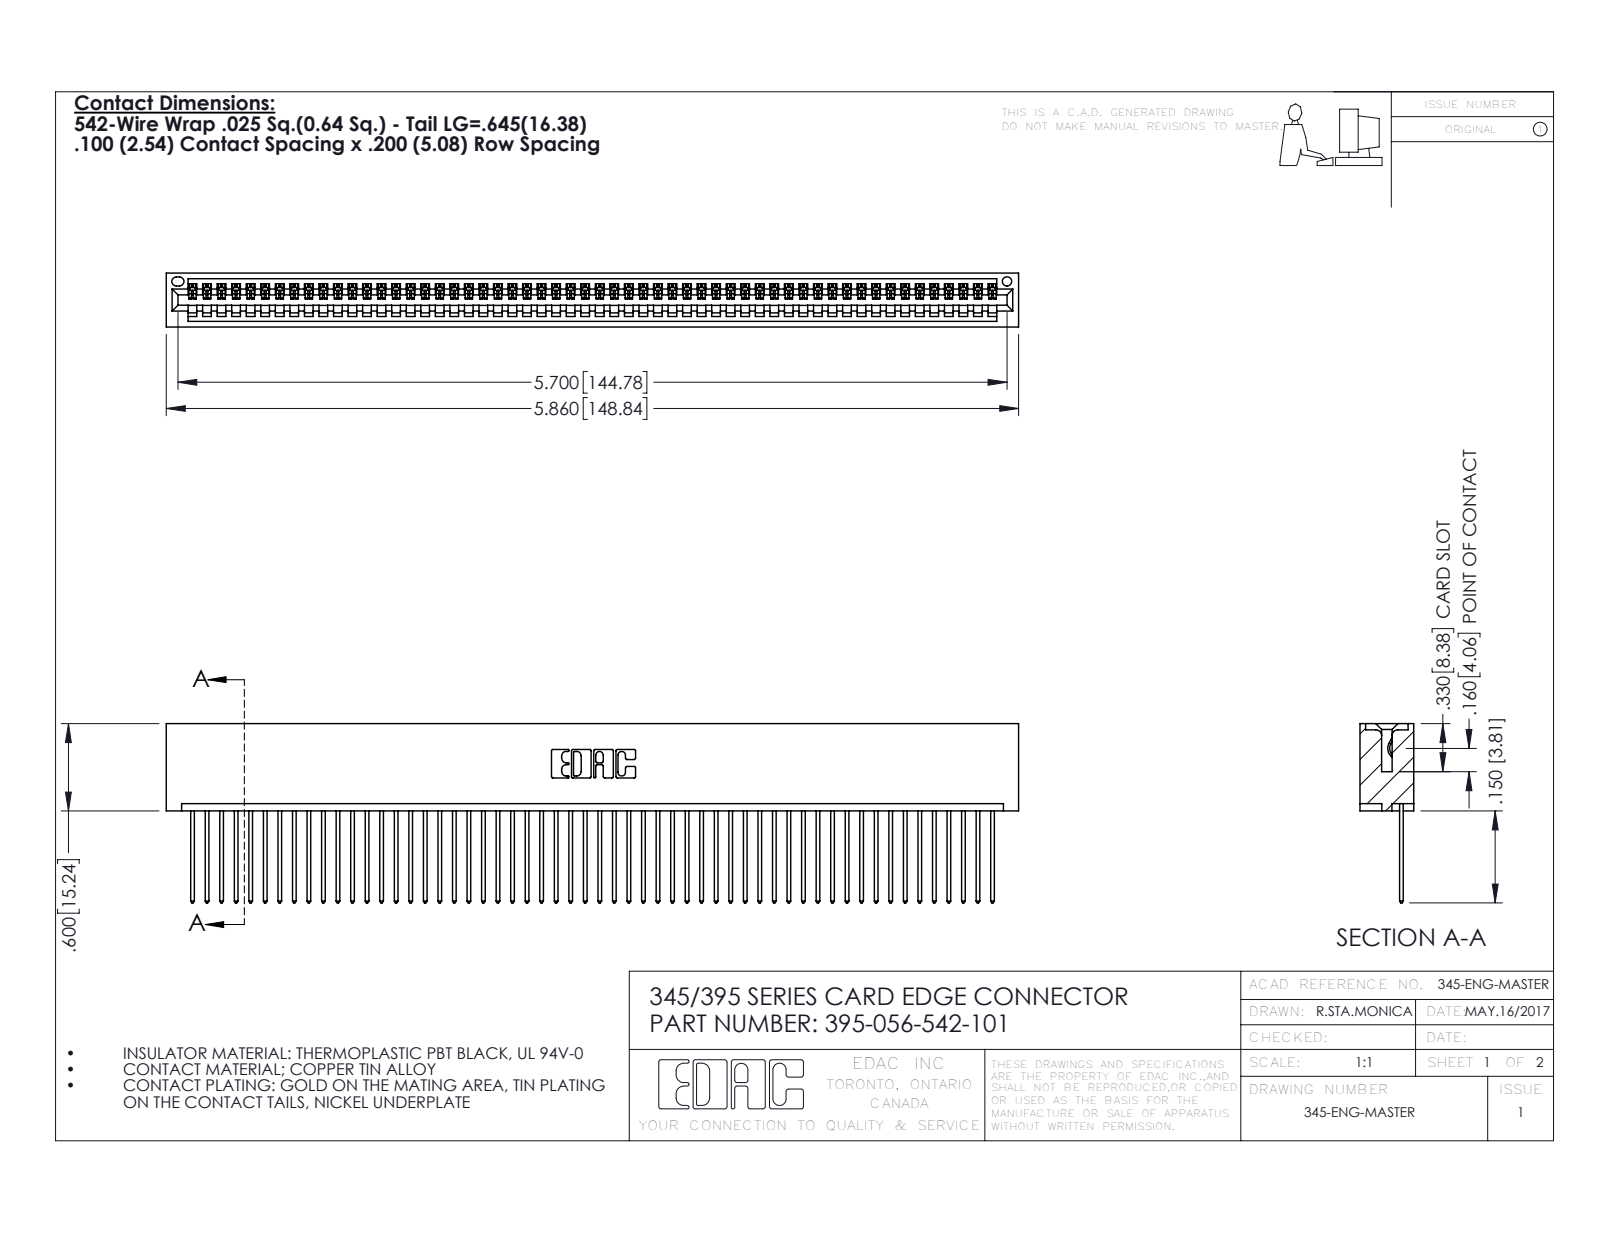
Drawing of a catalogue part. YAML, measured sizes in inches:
part_name: "345 Part_No Mounting Lugs; 395-056-542-101; 345-292-001_345-293-142"
step_written_by: "SolidWorks 2016 (CONFIG_CONTROL_DESIGN)"
units: inches
bodies: {solids: 57, faces: 3366, planar: 2316, cylindrical: 1050, other: 0}
overall_size: [5.86, 1.232, 0.37]
volume: 0.913
surface_area: 32.63
round_holes:
  - {diameter: 0.064, count: 1}
partial_cylinders:
  - {radius: 0.006, count: 112}
  - {radius: 0.01, count: 112}
  - {radius: 0.01, count: 22}
  - {radius: 0.007, count: 6}
  - {radius: 0.031, count: 6}
  - {radius: 0.026, count: 3}
  - {radius: 0.031, count: 2}
  - {radius: 0.04, count: 2}
face_to_face_distances: [0.072, 0.298, 0.098, 0.272, 0.025, 0.37, 0.2, 0.225, 0.149, 0.072]
